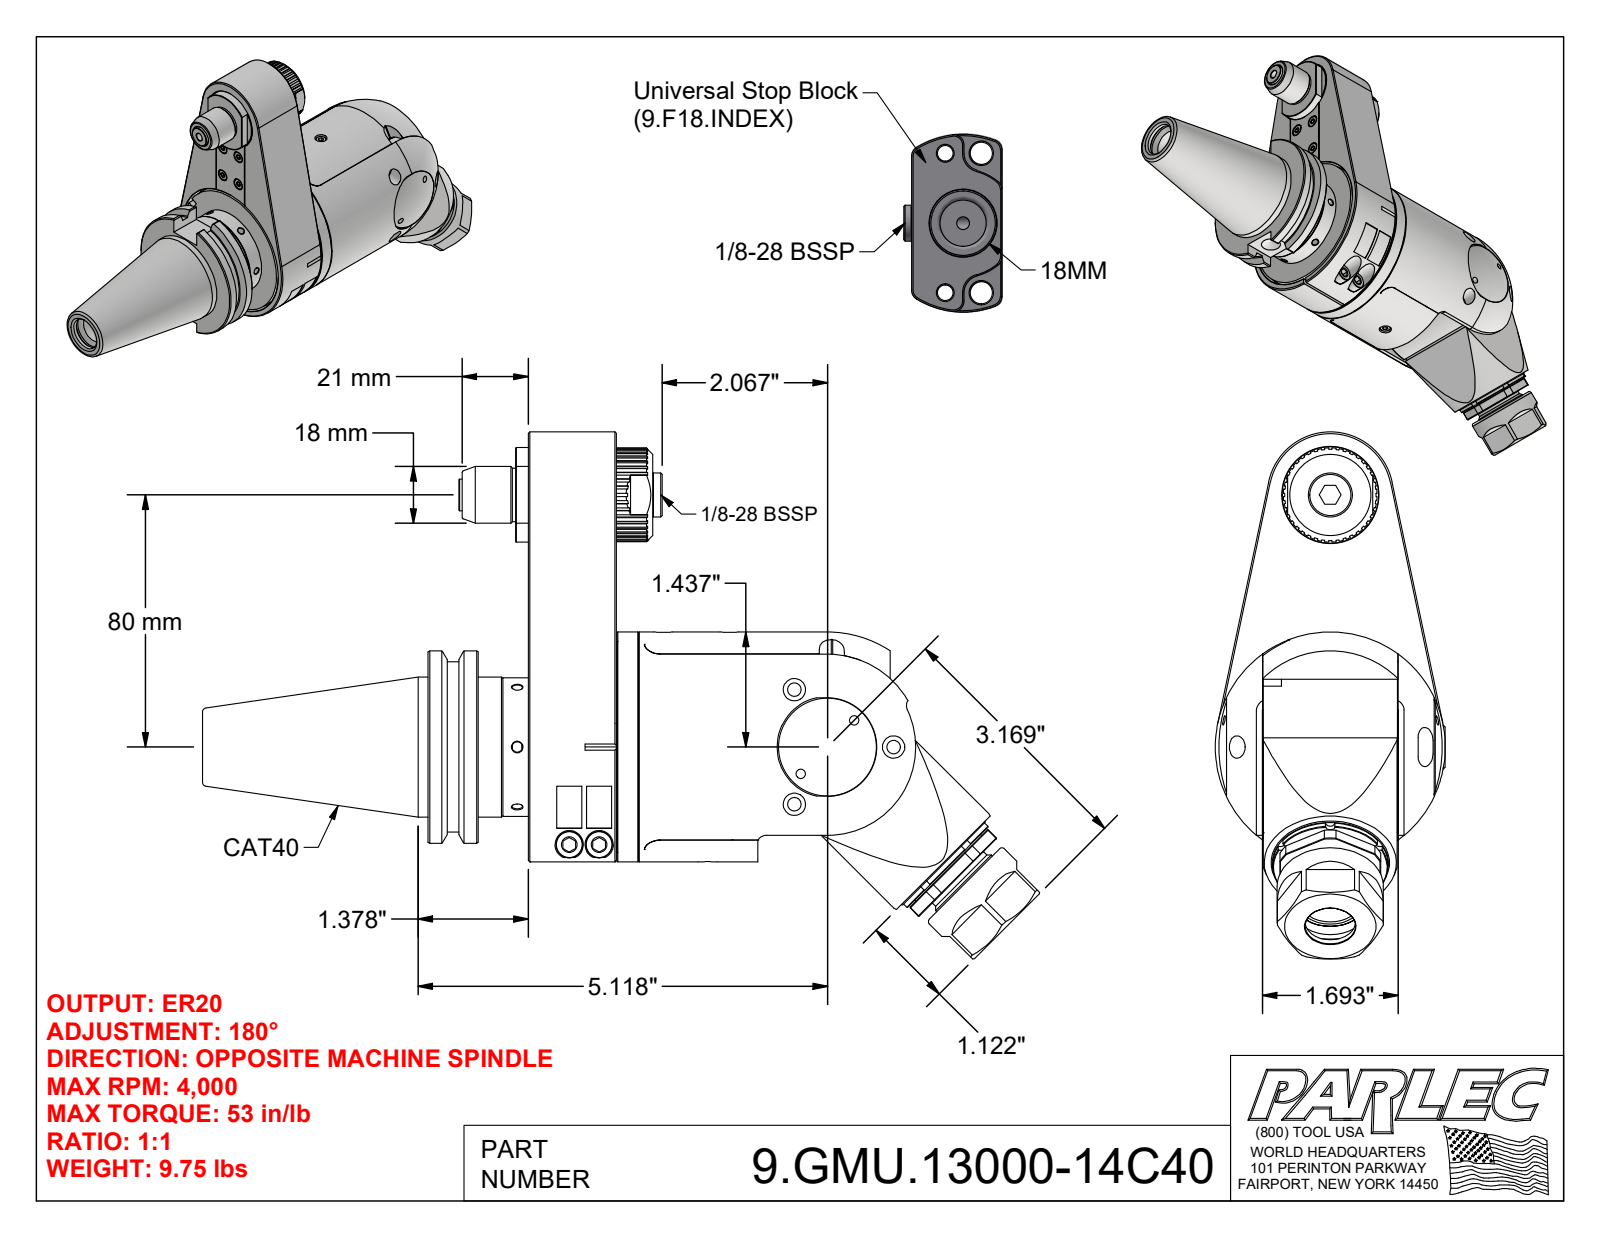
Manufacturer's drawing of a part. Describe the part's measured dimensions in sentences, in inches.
The part is named "9.GMU.13000-14C40; 9_GMU_13000; 9GMU13000_A; 9GMU13000_B (+1 more)". Its 3-D file was written by "Autodesk Inventor 2022 (AUTOMOTIVE_DESIGN)". It is 20 solids with 1061 faces: 455 planar, 313 cylindrical and 293 other. Overall it measures 10.462 by 6.588 by 2.874 inches. Its volume is 45.83 cubic inches and its surface area 222.1 square inches. Round holes: 35 of diameter 0.13, 9 of diameter 0.157, 9 of diameter 0.236, 5 of diameter 0.165, 3 of diameter 0.28, 2 of diameter 0.083, 2 of diameter 0.118, 2 of diameter 0.354, 2 of diameter 0.472, 2 of diameter 0.551, 2 of diameter 0.709, 2 of diameter 1.181. Round bosses or shafts: 4 of diameter 0.228, 3 of diameter 0.217, 2 of diameter 0.984, 2 of diameter 0.335, 2 of diameter 0.197, 1 of diameter 2.874, 1 of diameter 2.638, 1 of diameter 2.559. Partial cylindrical surfaces (rounded edges, fillets, slot ends): 6 of radius 0.059, 6 of radius 0.089, 6 of radius 0.142, 4 of radius 0.197, 3 of radius 0.118, 2 of radius 0.085, 1 of radius 0.02, 1 of radius 0.079. The main face-to-face distances are 1.102, 0.28, 1.693, 0.823, 0.626, 0.098, 1.535, 0.181, 2.638, 2.358. The hole center spacings are 0.787, 0.576, 0.779, 0.945, 0.194, 0.206, 0.959, 0.372.
